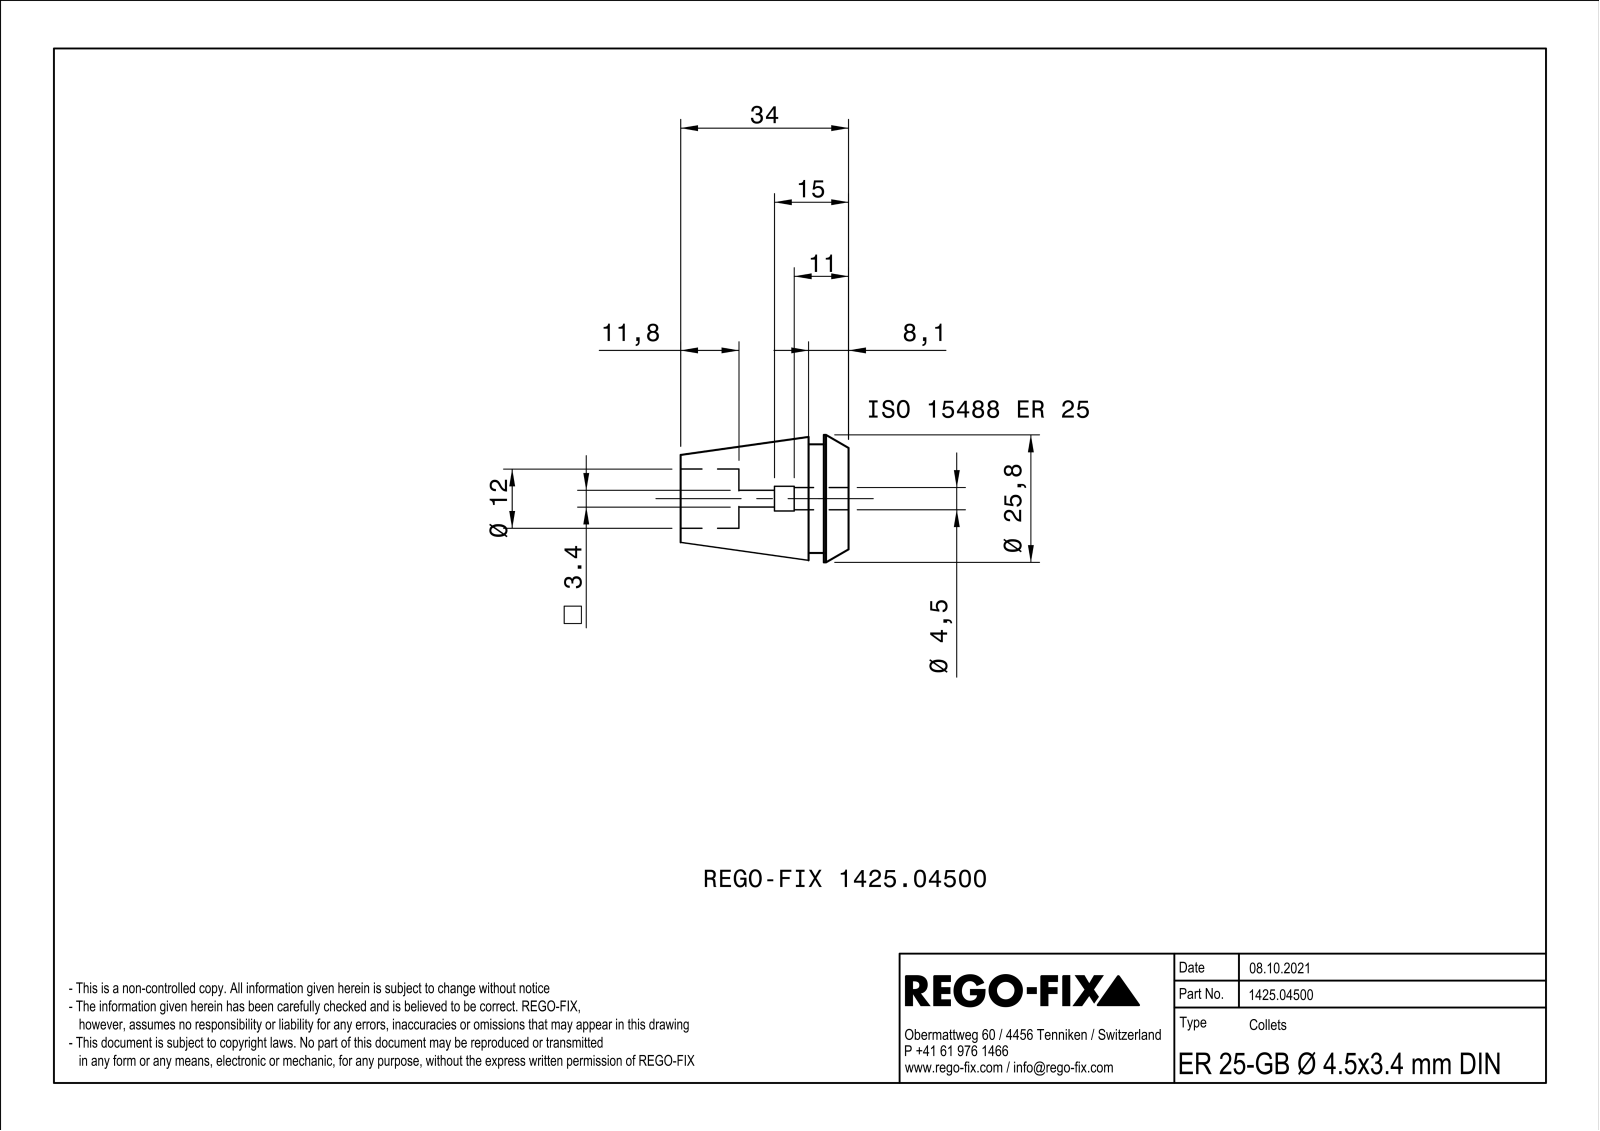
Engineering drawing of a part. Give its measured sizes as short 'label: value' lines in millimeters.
name: NOCUT
written by: SIEMENS PLM Software Solid Edge ST10 (AUTOMOTIVE_DESIGN)
unit: mm
bodies: 1 solid, 152 faces (68 planar, 32 cylindrical, 52 other)
size: 34 × 25.79 × 25.79
volume: 9 629 mm³; area: 7 017 mm²
holes: 1× ⌀12
bosses: 1× ⌀25.8, 1× ⌀22
rounds: 1× R1.9, 1× R2.25, 1× R2.5
face distances: 0.8, 5, 34, 29, 8.1, 3.1, 25.9, 22.2, 17.2, 14.1
